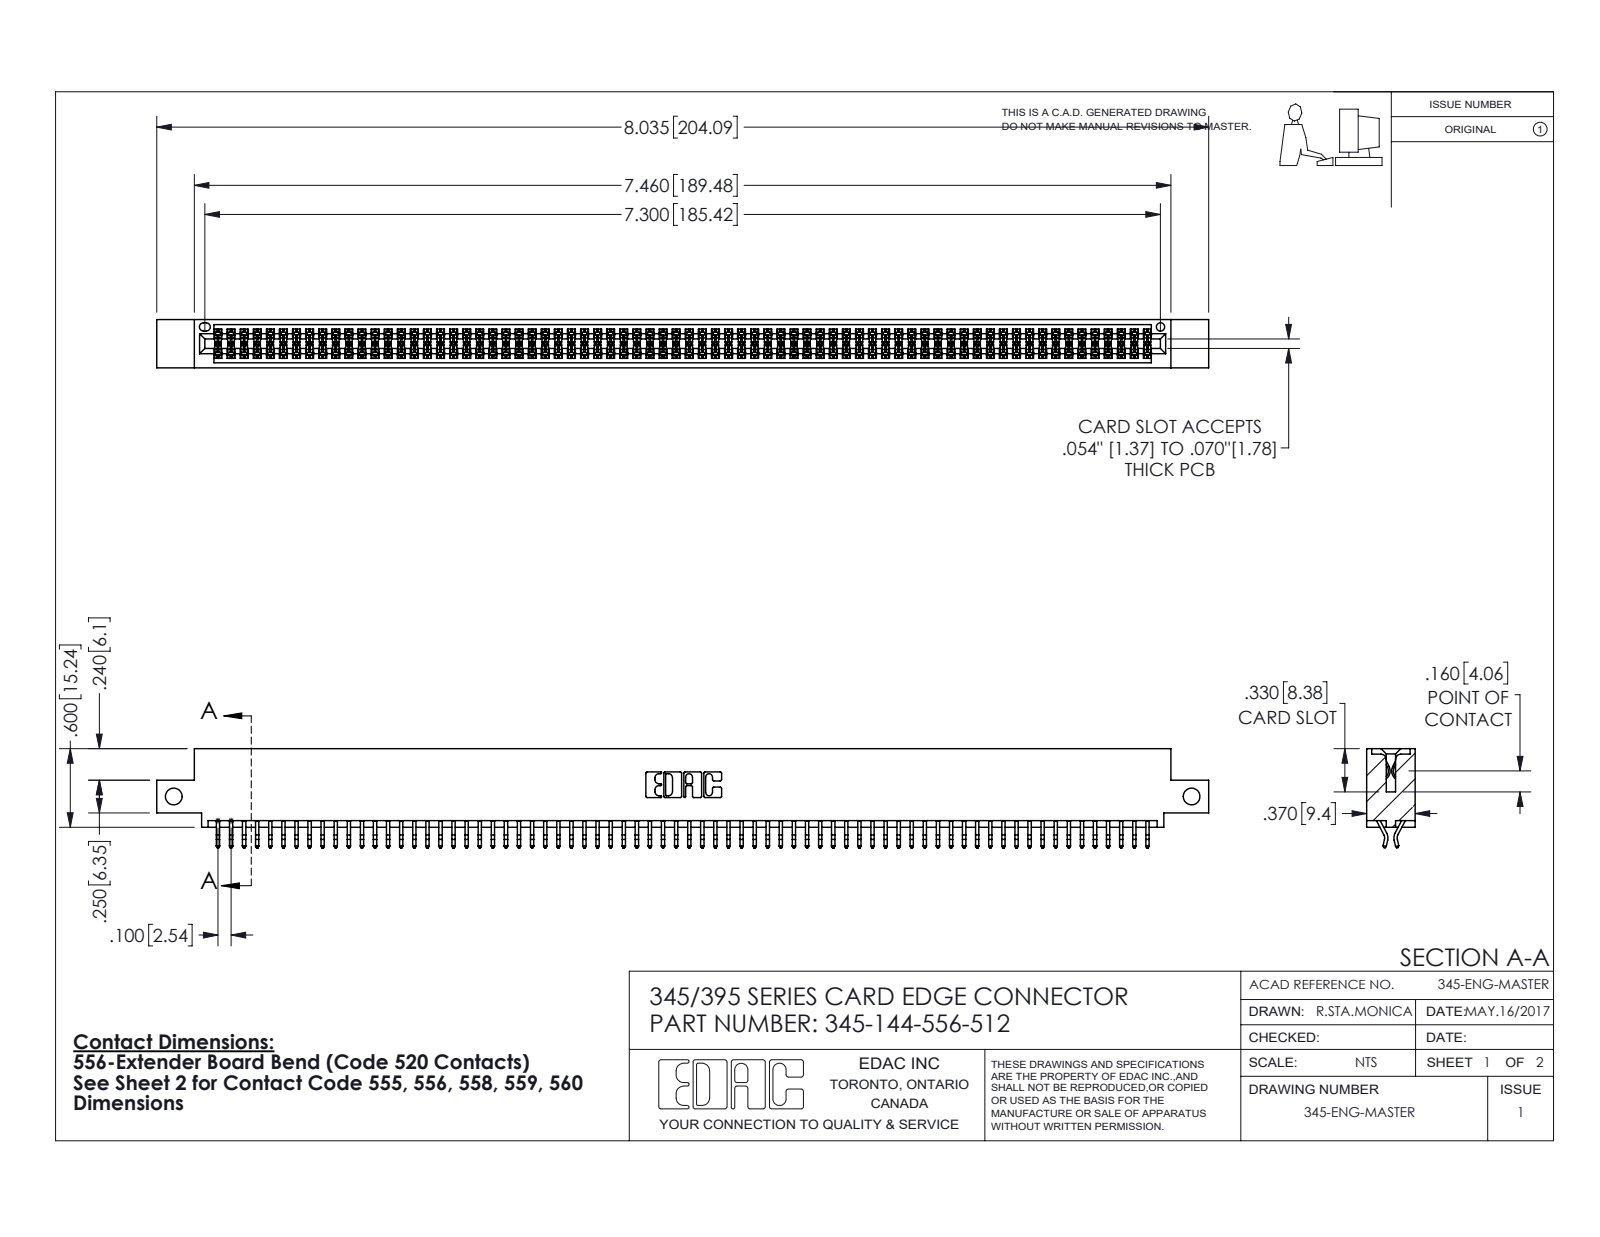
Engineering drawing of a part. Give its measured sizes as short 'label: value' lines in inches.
name: 345-292-001_556 Tail; 345-144-556-512; 345 Part_0.110 Offset - Side Mount
written by: SolidWorks 2016 (CONFIG_CONTROL_DESIGN)
unit: in
bodies: 145 solids, 8194 faces (5412 planar, 2782 cylindrical, 0 other)
size: 8.035 × 0.757 × 0.37
volume: 1.217 in³; area: 46.32 in²
holes: 2× ⌀0.128, 1× ⌀0.064
rounds: 216× R0.006, 22× R0.01, 6× R0.007, 6× R0.031, 3× R0.026, 2× R0.01, 2× R0.014, 2× R0.019
face distances: 0.298, 0.072, 0.37, 0.2, 0.025, 0.098, 0.272, 0.225, 0.175, 0.149
hole spacings: 7.775
